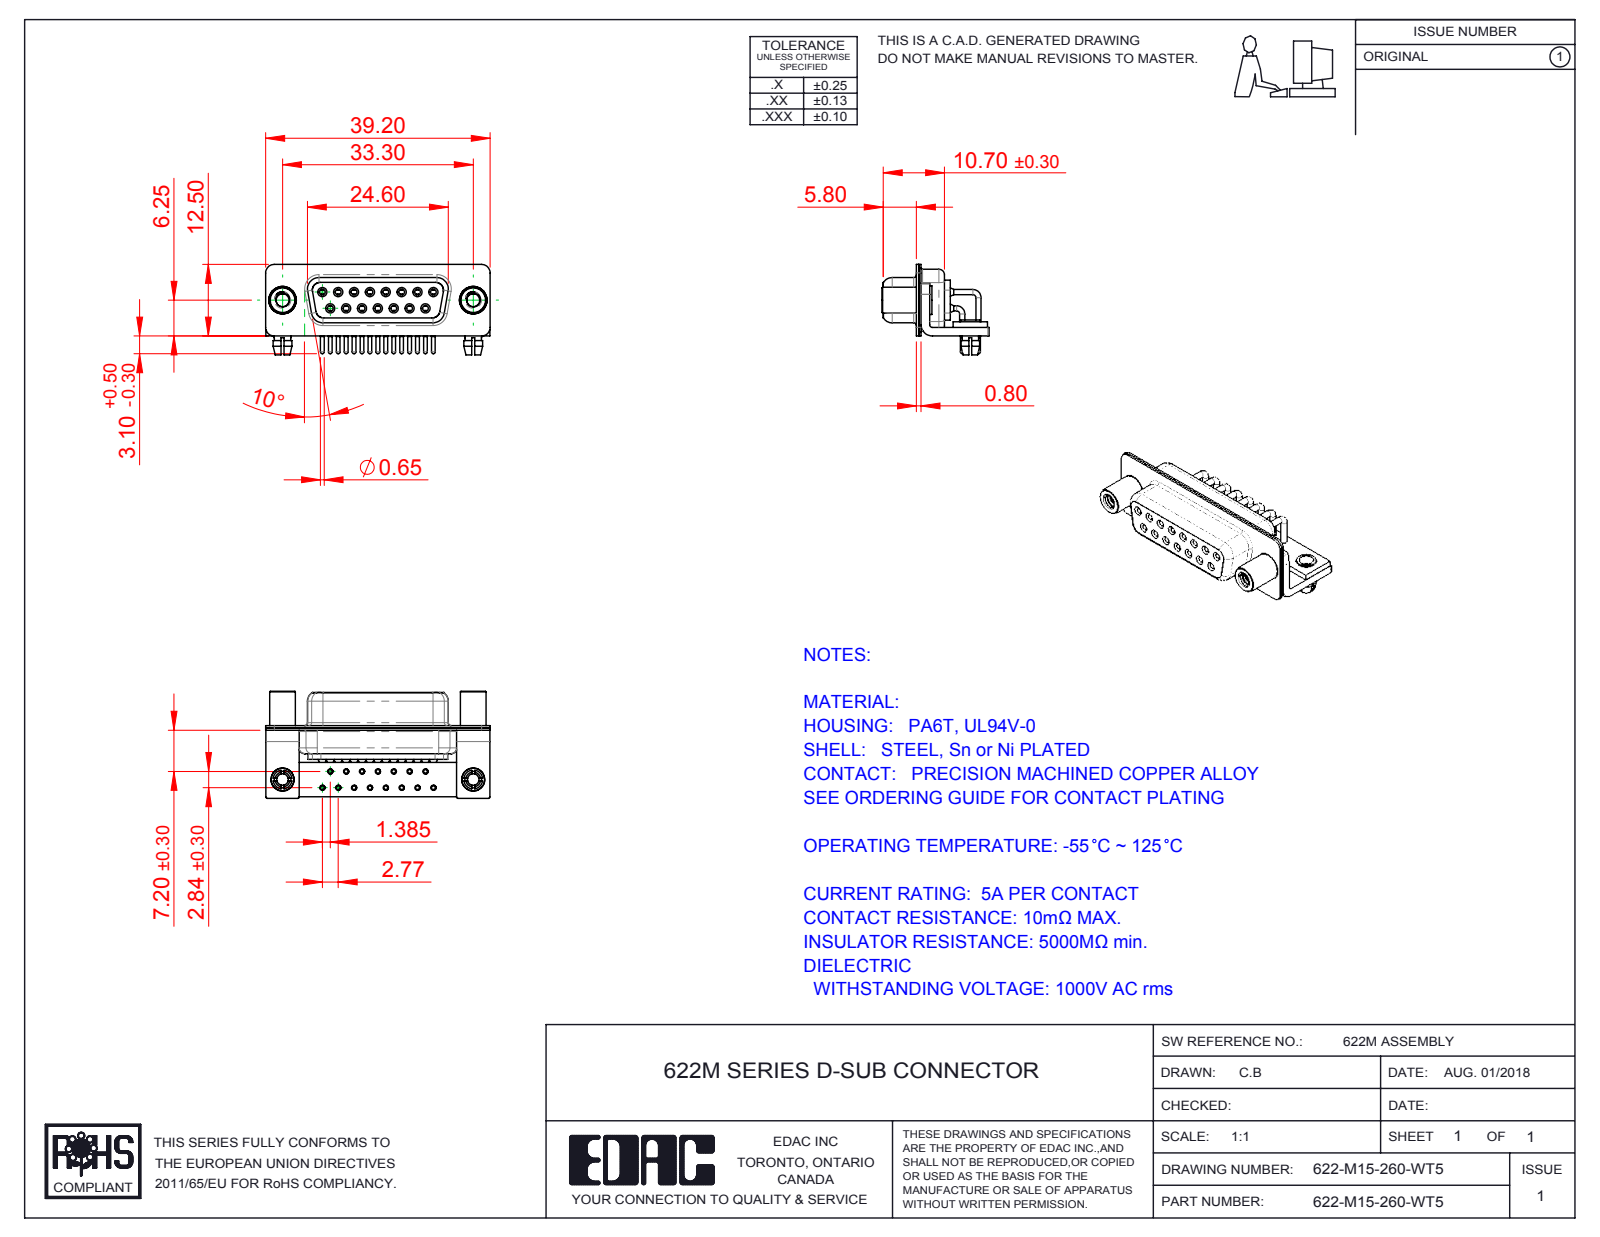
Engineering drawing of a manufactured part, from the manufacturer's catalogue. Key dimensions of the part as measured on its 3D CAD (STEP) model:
Part name (STEP PRODUCT): 622M Board Lock; 622M Shell Rear_15 Contacts; 622M Stabilizer Board_15 Contacts; 622M Shell Front_15 Contacts (+6 more)
STEP written by: SolidWorks 2016 (CONFIG_CONTROL_DESIGN)
Units: millimetres
Bodies: 25 solids, 1296 faces (368 planar, 608 cylindrical, 320 other)
Overall size (bounding box): 39.2 × 18.7 × 15.8
Volume: 3 146 mm³ · Surface area: 8 070 mm²
Round holes (diameter × count): ⌀2 ×17, ⌀0.9 ×15, ⌀1 ×15, ⌀1.1 ×15, ⌀1.7 ×15, ⌀1.8 ×15, ⌀2.26 ×2, ⌀2.5 ×2, ⌀3.2 ×2, ⌀4 ×2, ⌀4.8 ×2
Round bosses / shafts (diameter × count): ⌀0.9 ×22, ⌀1.6 ×15, ⌀1.5 ×15, ⌀0.65 ×15, ⌀5 ×2, ⌀4.9 ×2, ⌀4.5 ×2, ⌀4 ×2
Partial cylindrical surfaces — rounded edges, fillets, slot ends (radius × count): R0.25 ×16, R1.5 ×16, R2 ×13, R1.35 ×8, R1.6 ×8, R0.5 ×5, R0.6 ×4, R0.65 ×4
Main face-to-face distances: 0.4, 2.3, 1.9, 0.8, 9.35, 1.5, 1, 1.45, 8.95, 0.85
Hole centre spacings: 3.16, 2.77, 5.54, 8.31, 11.08, 5.03, 5.04, 7.48
